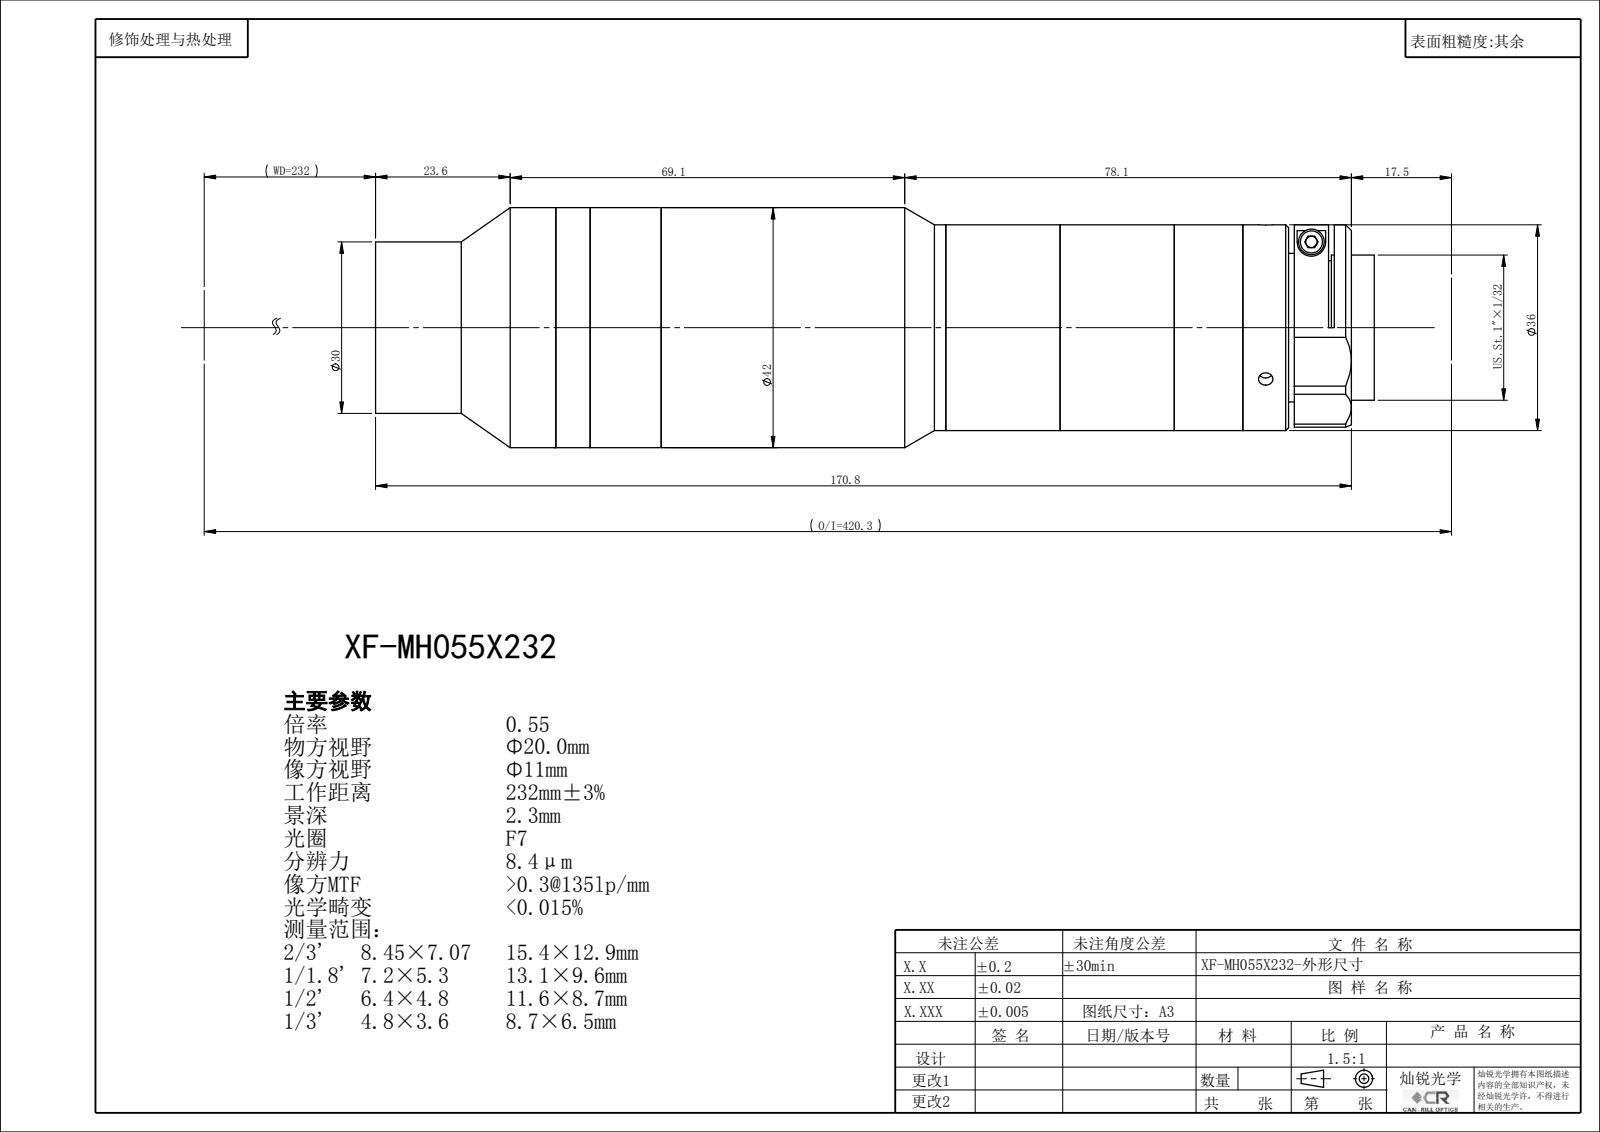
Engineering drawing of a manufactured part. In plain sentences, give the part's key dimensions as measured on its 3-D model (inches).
The part is named "XF-MH055X232". Its 3-D file was written by "SolidWorks 2022 (CONFIG_CONTROL_DESIGN)". It is 0 solids with 137 faces: 67 planar, 46 cylindrical and 24 other. Overall it measures 6.879 by 1.654 by 1.654 inches. Round holes: 3 of diameter 0.098, 1 of diameter 0.882, 1 of diameter 0.945, 1 of diameter 1.039. Round bosses or shafts: 1 of diameter 1.654, 1 of diameter 1.417, 1 of diameter 1.339, 1 of diameter 1.181, 1 of diameter 1. The main face-to-face distances are 0.059, 1.157, 1.216, 1.575, 2.732, 2.791, 2.283, 0.709, 0.448, 0.507.
